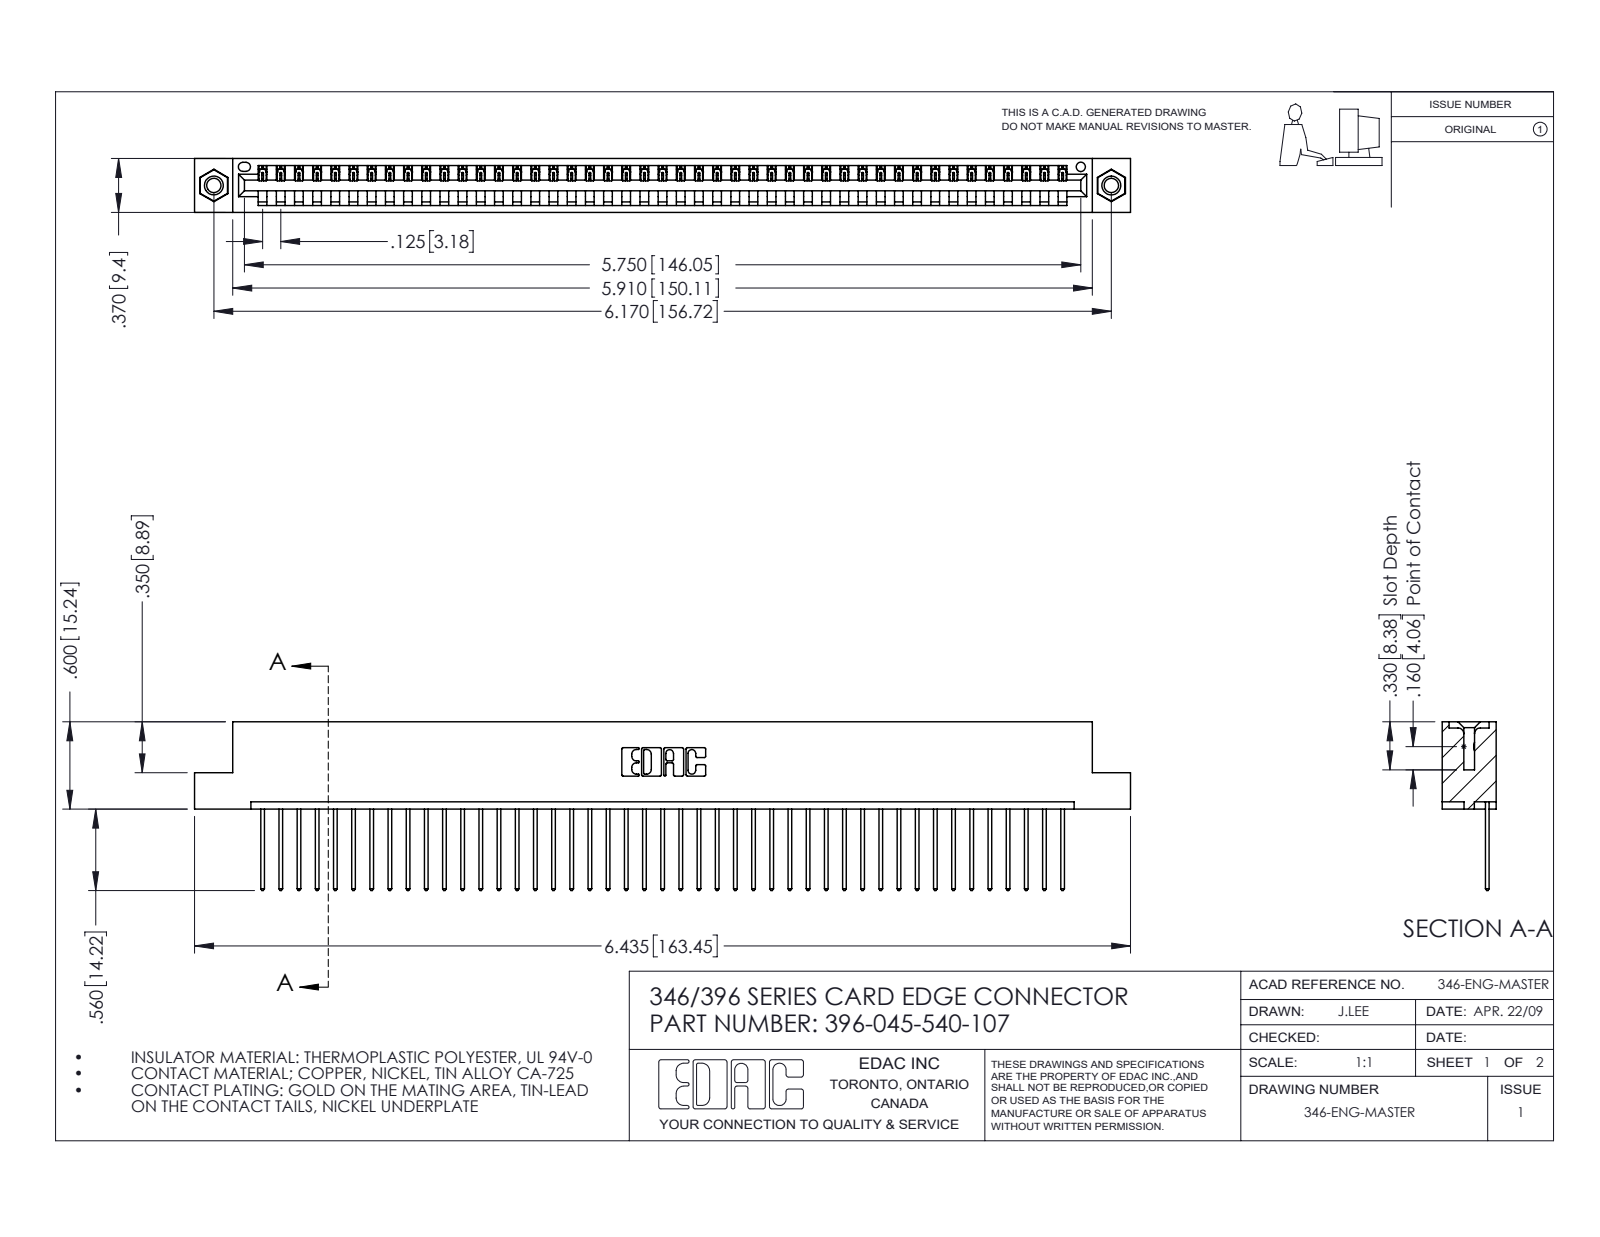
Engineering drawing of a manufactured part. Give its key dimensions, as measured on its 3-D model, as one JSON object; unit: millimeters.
{"part_name": "345-292-001_345-293-140; 345-250-001_345-250-005-103; 396-045-540-107; 346 Part_Flush Mounting Lugs - 0.156 Dia-TI", "step_written_by": "SolidWorks 2016 (CONFIG_CONTROL_DESIGN)", "units": "millimeters", "bodies": {"solids": 48, "faces": 2792, "planar": 1908, "cylindrical": 868, "other": 16}, "overall_size": [163.4, 29.5, 9.4], "volume_mm3": 15700, "surface_area_mm2": 20150, "round_holes": [[2.5, 2], [3.2, 2], [4, 2], [1.6, 1]], "round_bosses_or_shafts": [[3.9, 2]], "partial_cylinders_radius": [[0.2, 90], [0.3, 90], [0.3, 22], [0.2, 6], [0.8, 6], [0.7, 3], [0.8, 2], [1, 2]], "face_to_face_distances": [1.2, 8.2, 9.4, 6.4, 1.8, 7.6, 0.6, 3.8, 5.6, 2.5], "hole_center_spacings": [6.2, 151.4, 156.7]}
